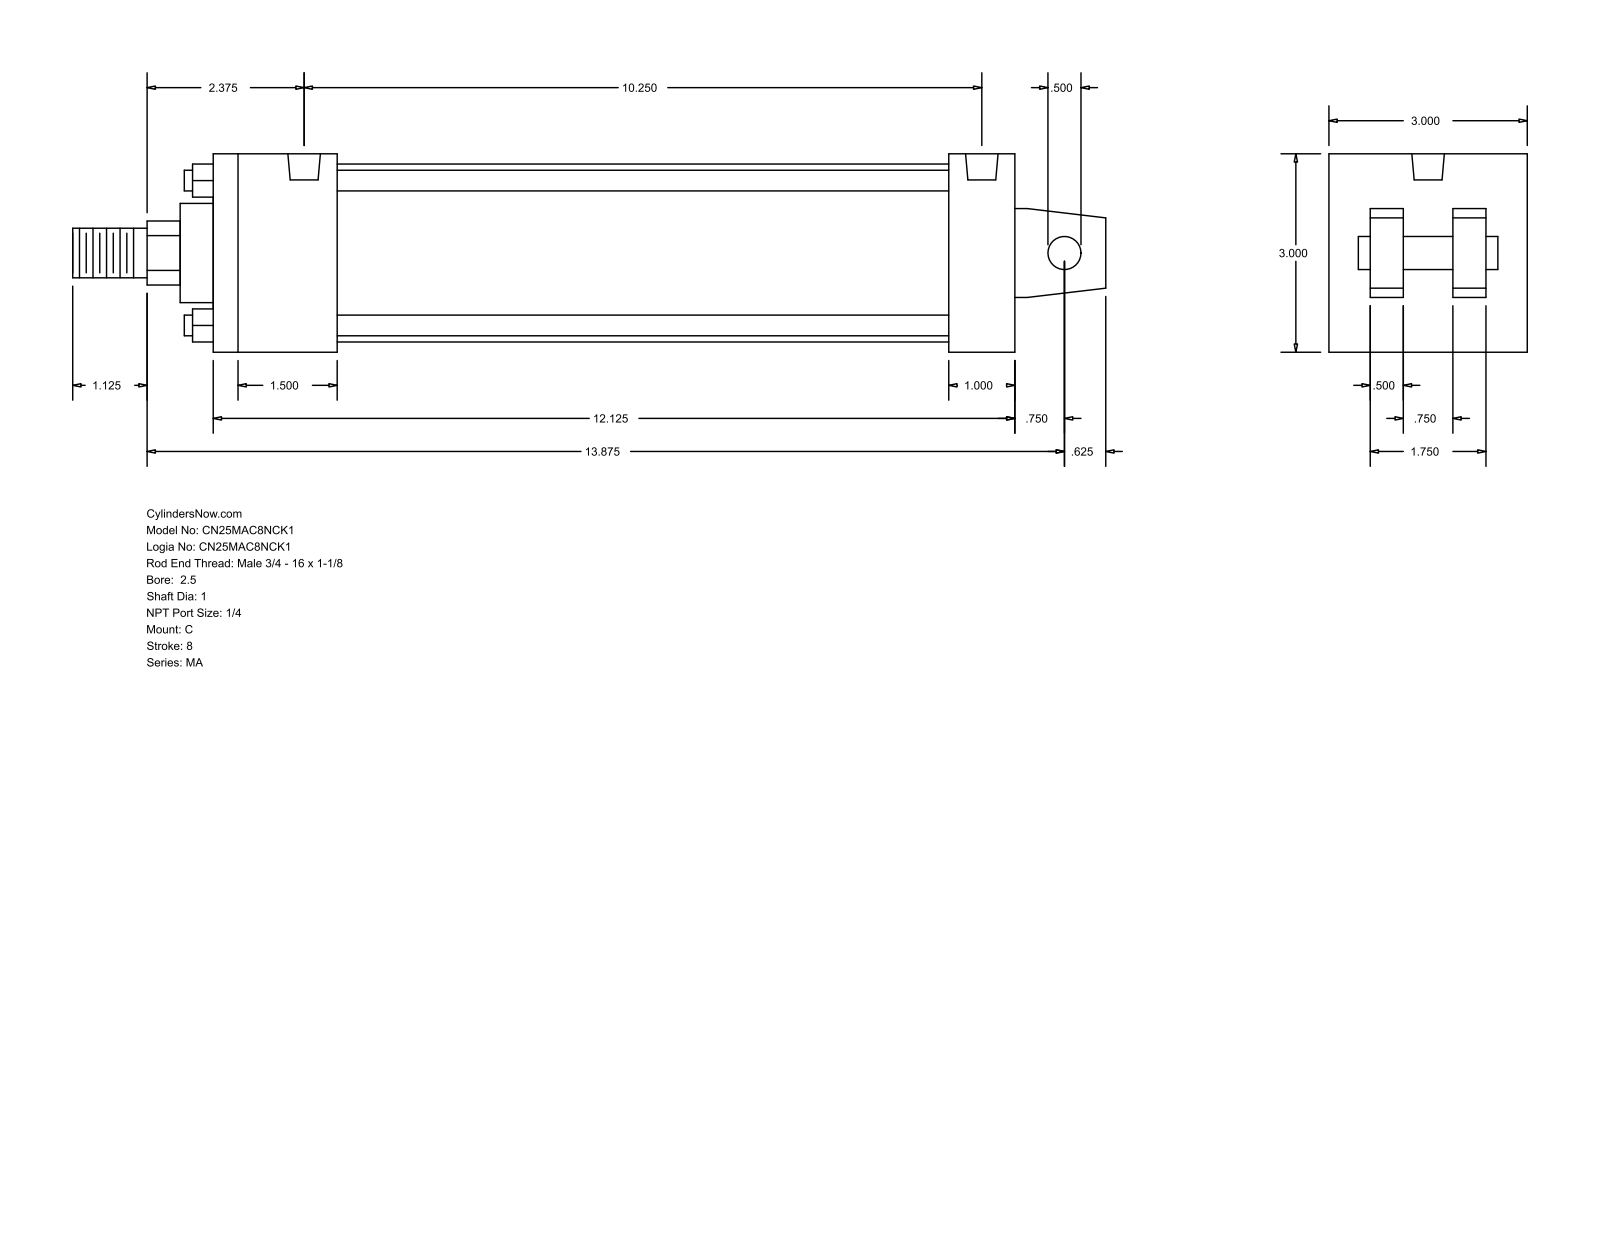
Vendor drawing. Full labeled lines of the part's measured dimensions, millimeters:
Part name (STEP PRODUCT): MA_C__0250_1
STEP written by: GSSL Pune (CONFIG_CONTROL_DESIGN)
Units: millimetres
Bodies: 0 solids, 103 faces (76 planar, 27 cylindrical, 0 other)
Overall size (bounding box): 396.88 × 76.2 × 76.2
Round holes (diameter × count): ⌀7.94 ×4, ⌀12.49 ×2
Round bosses / shafts (diameter × count): ⌀7.94 ×4, ⌀68.33 ×1, ⌀38.1 ×1, ⌀25.4 ×1, ⌀19.05 ×1, ⌀12.7 ×1
Partial cylindrical surfaces — rounded edges, fillets, slot ends (radius × count): R12.29 ×1
Main face-to-face distances: 76.2, 307.98, 47.63, 12.7, 60.33, 15.87, 25.4, 28.57, 282.58, 234.95
Hole centre spacings: 260.35
